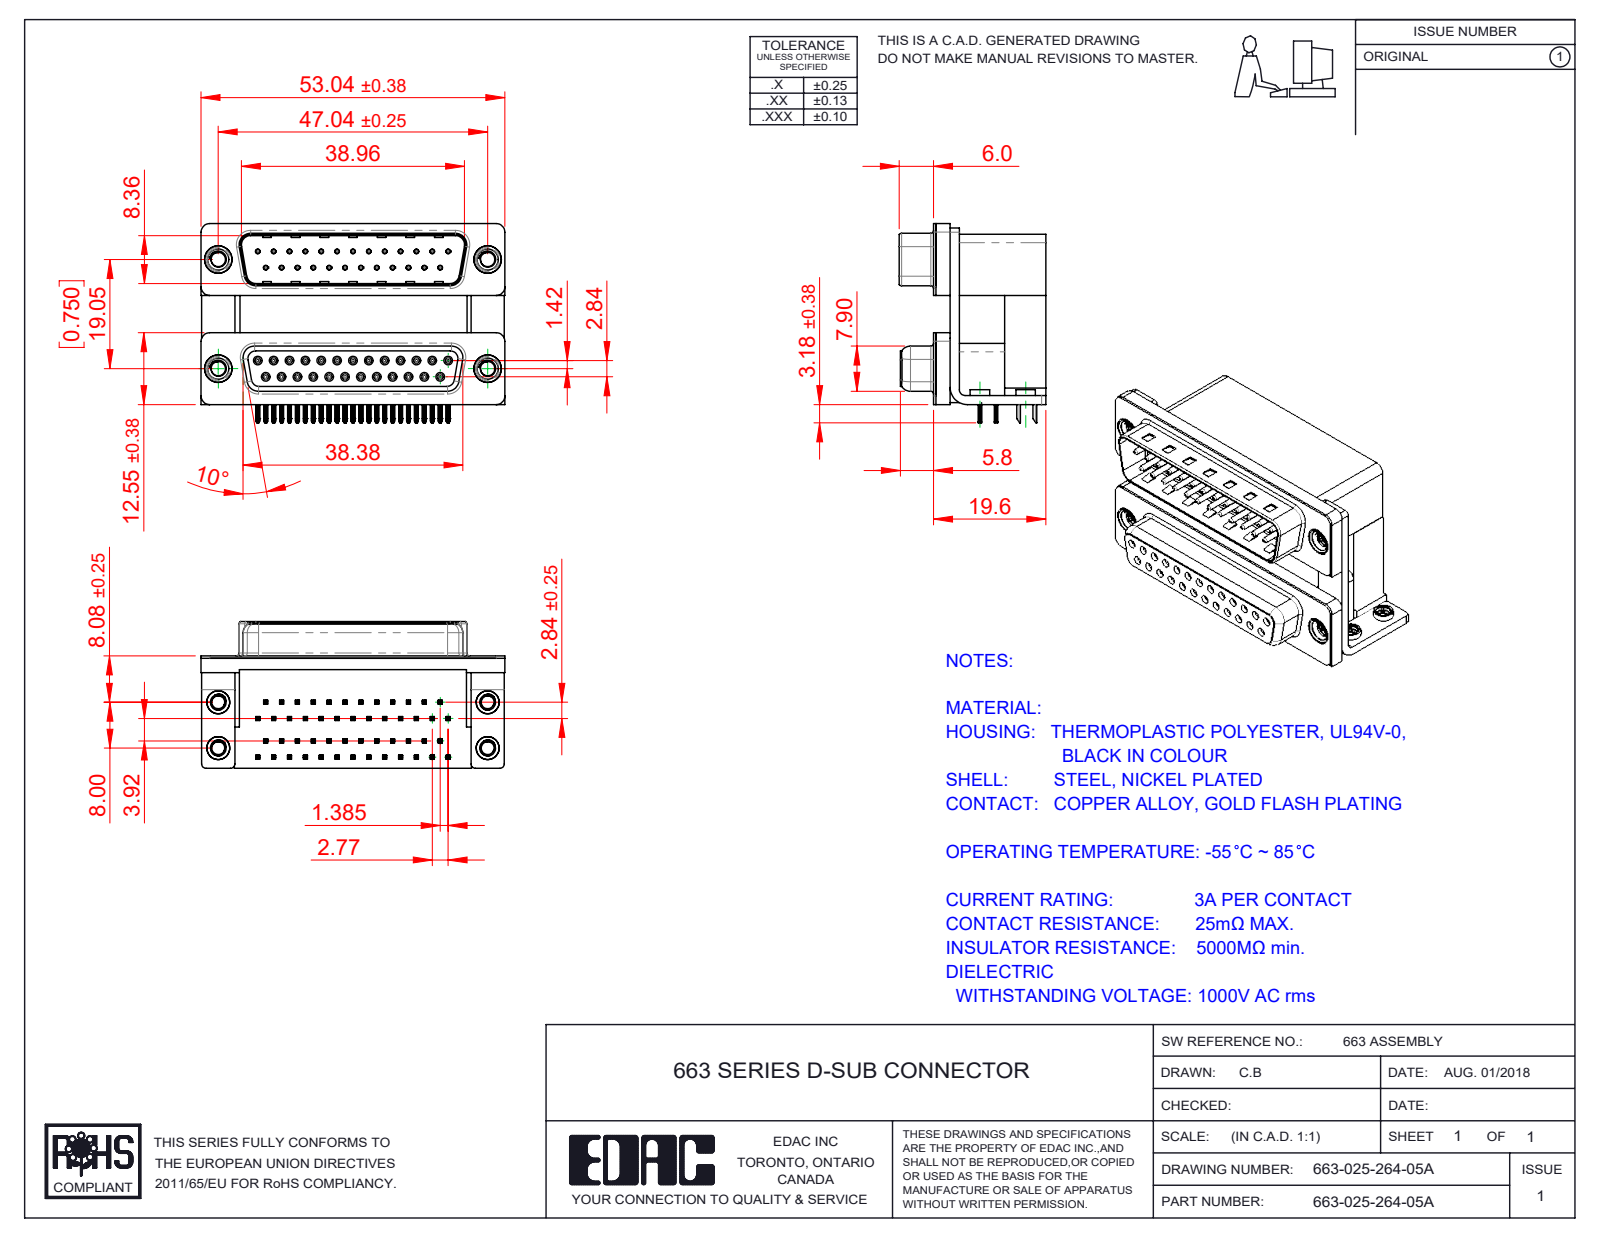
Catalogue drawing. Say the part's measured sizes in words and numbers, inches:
The part is named "663 Housing Upper_25 Contacts M; 663 Threaded Rivet_M3; 663 Contact Bottom Upper_M; 663 Housing Spacer_25 Contacts M (+8 more)". Its 3-D file was written by "SolidWorks 2020 (CONFIG_CONTROL_DESIGN)". It is 65 solids with 6347 faces: 3269 planar, 1627 cylindrical and 1451 other. Overall it measures 2.088 by 1.369 by 1.008 inches. Its volume is 1.379 cubic inches and its surface area 37.44 square inches. Round holes: 50 of diameter 0.031, 25 of diameter 0.014, 25 of diameter 0.035, 4 of diameter 0.089, 4 of diameter 0.098, 4 of diameter 0.108, 4 of diameter 0.126, 4 of diameter 0.138, 4 of diameter 0.157, 4 of diameter 0.189, 4 of diameter 0.197. Round bosses or shafts: 25 of diameter 0.047, 25 of diameter 0.03, 4 of diameter 0.193, 4 of diameter 0.187, 4 of diameter 0.157, 4 of diameter 0.154, 4 of diameter 0.134. Partial cylindrical surfaces (rounded edges, fillets, slot ends): 200 of radius 0.004, 100 of radius 0.006, 100 of radius 0.01, 50 of radius 0.005, 50 of radius 0.014, 25 of radius 0.013, 14 of radius 0.059, 12 of radius 0.011. The main face-to-face distances are 0.756, 0.016, 0.283, 0.472, 0.421, 0.657, 0.374, 0.098, 0.737, 1.157. The hole center spacings are 0.124, 0.109, 0.218, 0.436, 0.327, 0.198, 0.545, 0.294.
